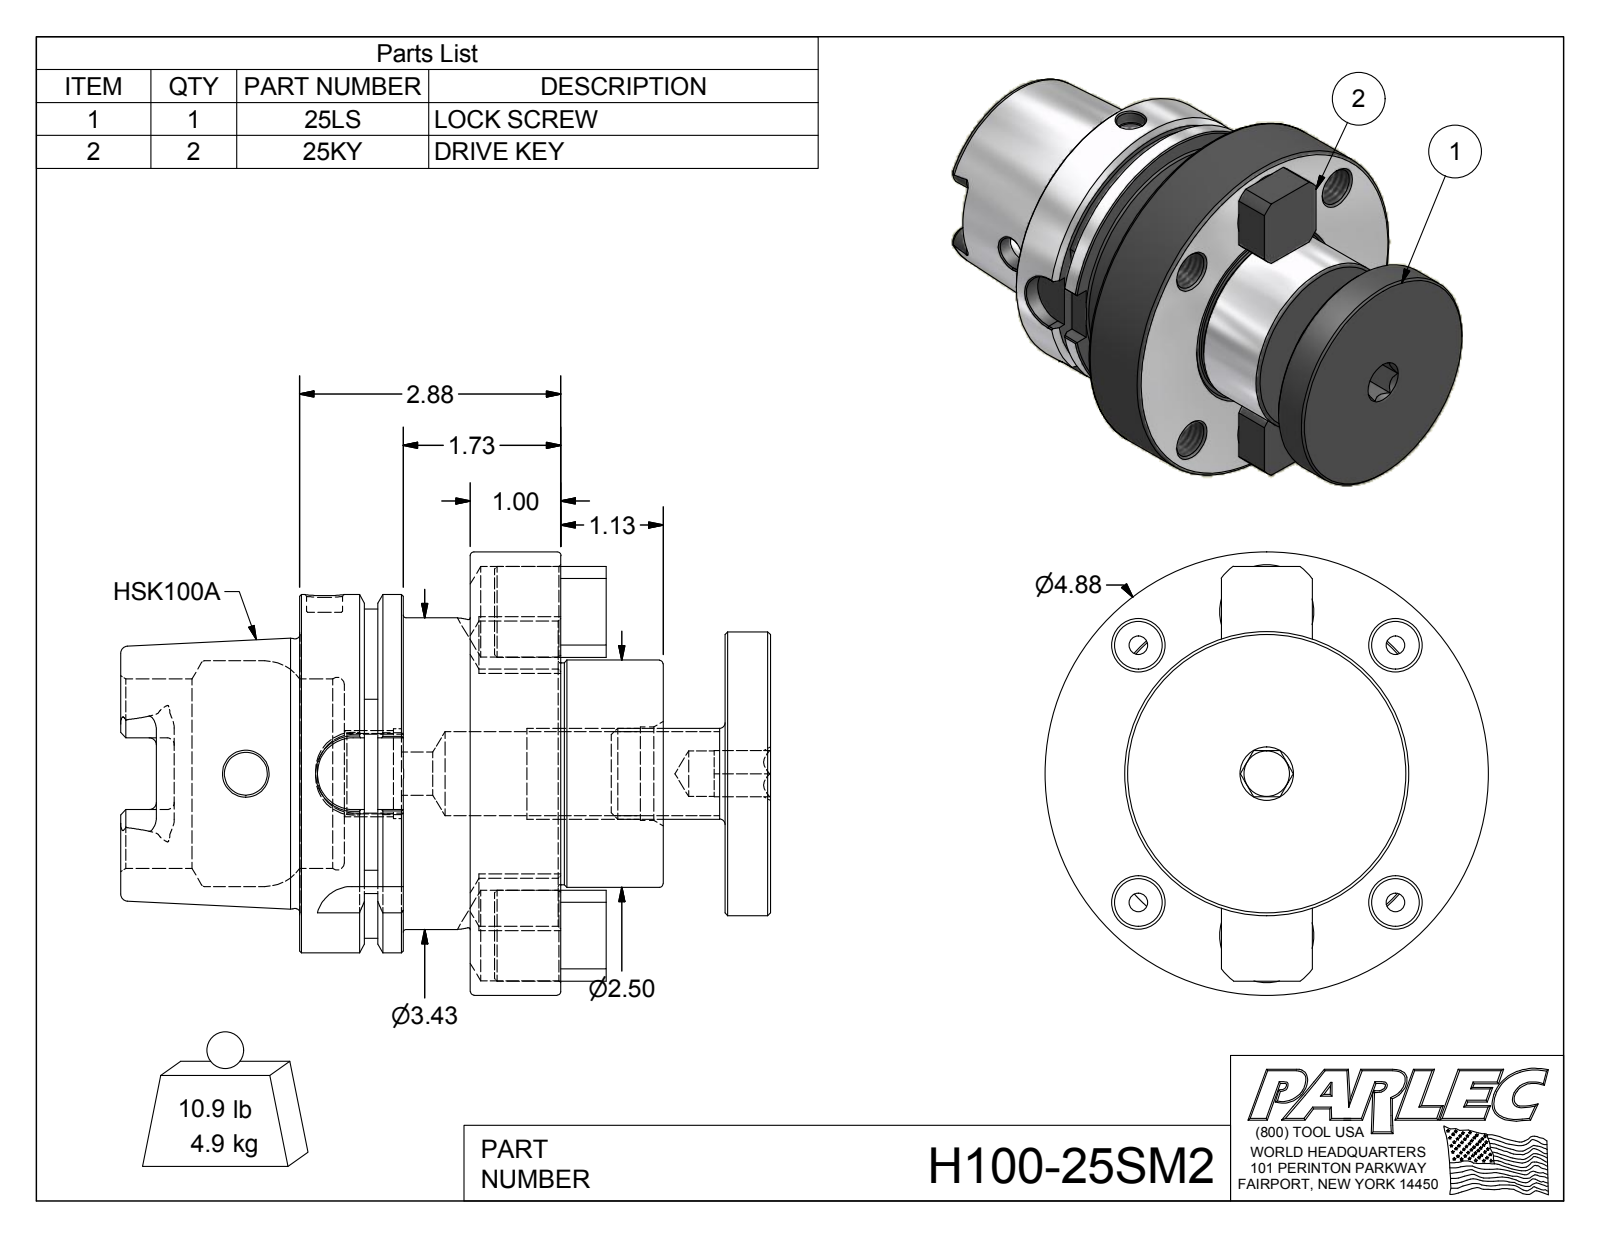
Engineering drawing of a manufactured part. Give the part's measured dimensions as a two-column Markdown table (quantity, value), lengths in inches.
| quantity | value |
| --- | --- |
| part name | H100-25SM2; 25LS; 25KY |
| STEP written by | Autodesk Inventor 2012 (AUTOMOTIVE_DESIGN) |
| units | inches |
| bodies | 4 solids, 203 faces (71 planar, 56 cylindrical, 76 other) |
| overall size | 7.149 × 4.875 × 4.875 |
| volume | 48.94 in³ |
| surface area | 183 in² |
| round holes (diameter × count) | 0.527 × 4, 0.472 × 2, 1 × 2, 0.394 × 1, 0.502 × 1, 0.881 × 1, 0.923 × 1, 0.985 × 1, 1.03 × 1, 2.087 × 1, 2.48 × 1 |
| round bosses / shafts (diameter × count) | 1 × 2, 4.875 × 1, 3.937 × 1, 3.425 × 1, 3.12 × 1, 2.967 × 1, 2.5 × 1, 2.44 × 1 |
| partial cylindrical surfaces (radius × count) | 0.079 × 6, 0.192 × 4, 0.394 × 4, 0.62 × 2, 1.811 × 1 |
| main face-to-face distances | 0.5, 1.805, 0.996, 3.301, 2.305, 2.801, 1.879, 2.875, 4.68, 5.18 |
| hole center spacings | 1.461, 2, 2.828, 3.493, 1.78, 4, 3.56 |
